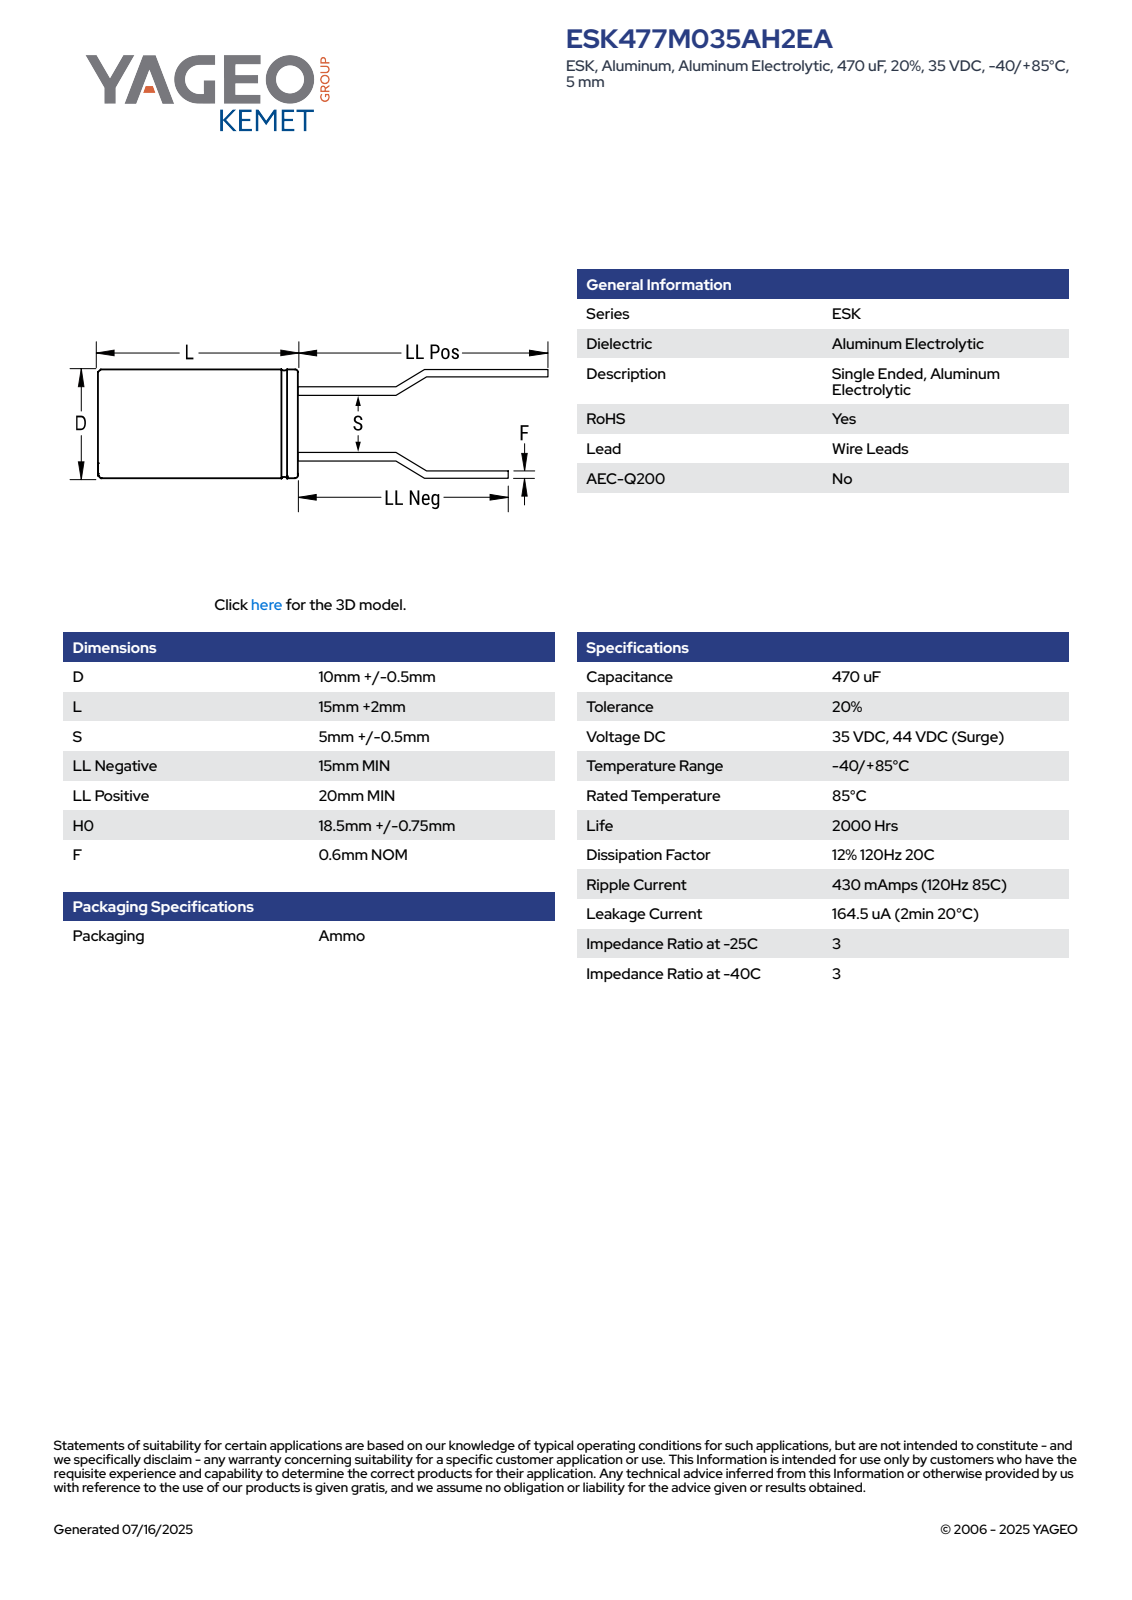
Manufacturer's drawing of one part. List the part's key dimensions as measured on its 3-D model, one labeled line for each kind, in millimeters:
Part name (STEP PRODUCT): CAR_KTRS_10X15_D10.5L17S5F0.6
STEP written by: SolidWorks 2014 (AUTOMOTIVE_DESIGN)
Units: millimetres
Bodies: 4 solids, 73 faces (61 planar, 8 cylindrical, 4 other)
Overall size (bounding box): 37.01 × 10.5 × 10.5
Volume: 1 470 mm³ · Surface area: 825 mm²
Round bosses / shafts (diameter × count): ⌀0.6 ×2, ⌀10.5 ×1
Main face-to-face distances: 17, 17.01, 32.01, 37.01, 32, 37, 15, 20, 5, 1.24
